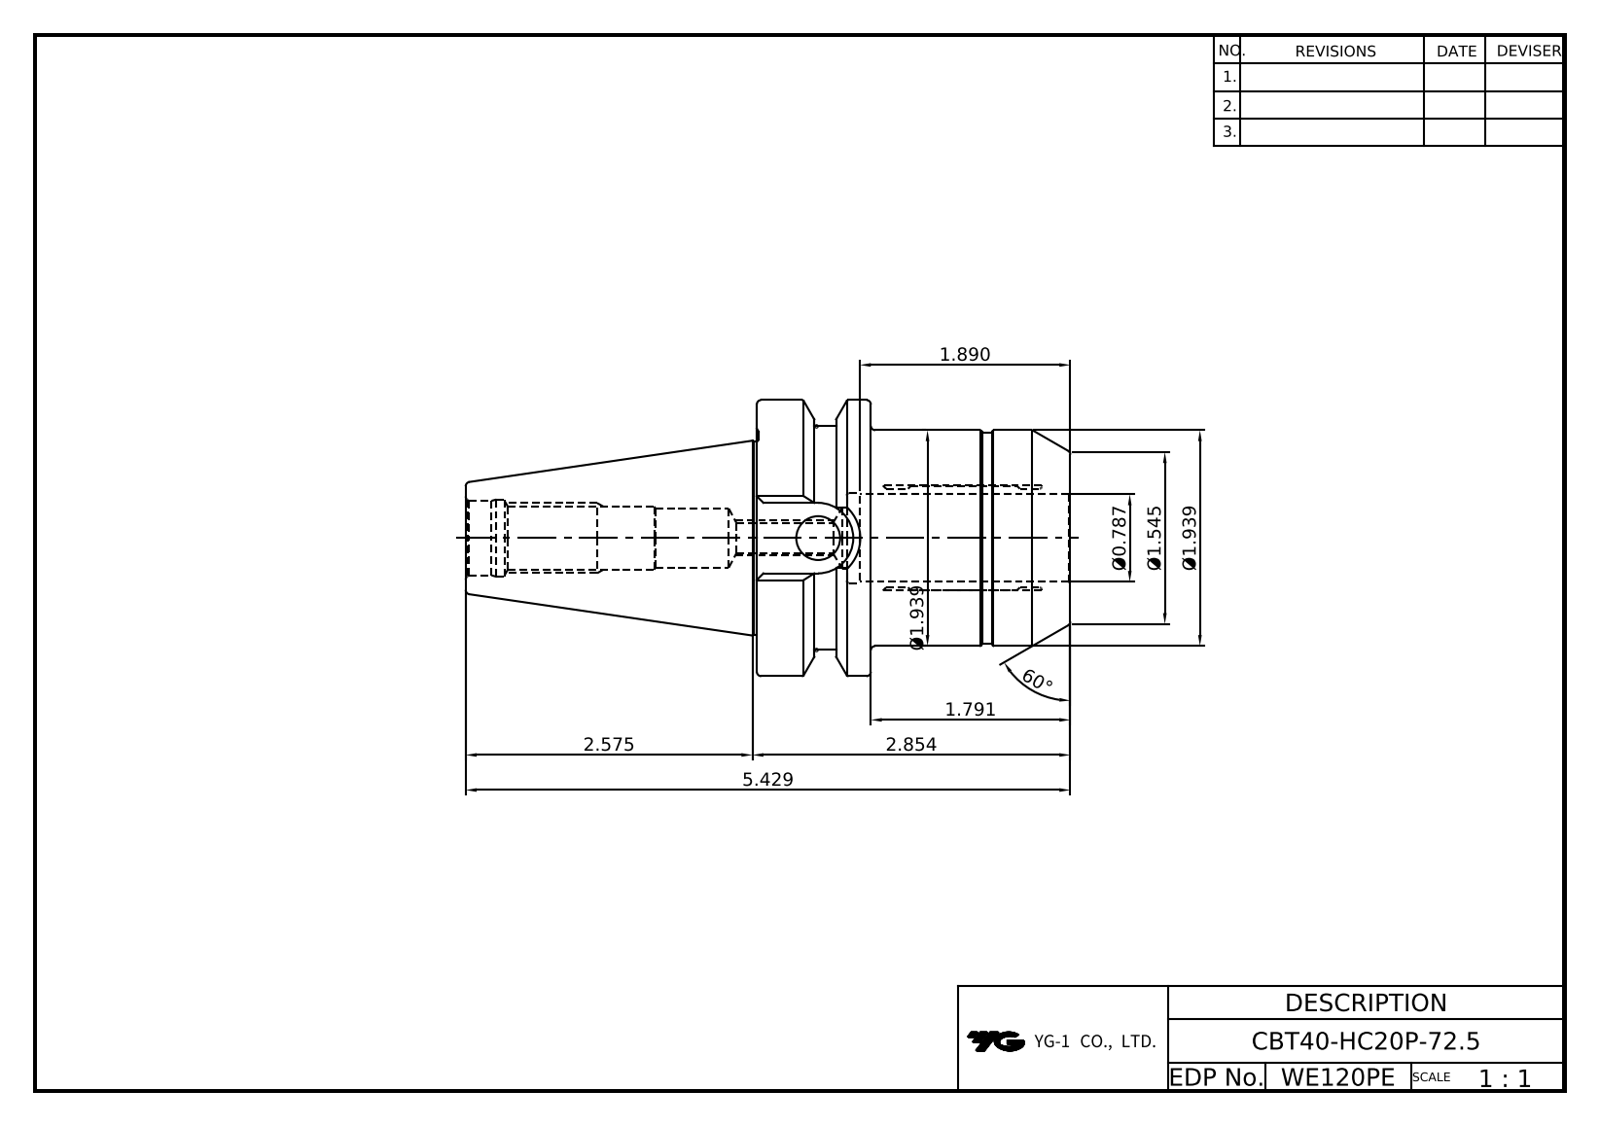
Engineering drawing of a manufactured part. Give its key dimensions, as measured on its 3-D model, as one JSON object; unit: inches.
{"part_name": "LO-CBT40-HC20P-72.5", "step_written_by": "Autodesk Inventor 2020 (AUTOMOTIVE_DESIGN)", "units": "inches", "bodies": {"solids": 1, "faces": 74, "planar": 24, "cylindrical": 19, "other": 31}, "overall_size": [5.429, 2.48, 2.48], "volume_in3": 11.66, "surface_area_in2": 49.04, "round_holes": [[0.272, 1], [0.531, 1], [0.545, 1], [0.551, 1], [0.669, 1], [0.693, 1], [0.787, 1], [0.807, 1]], "round_bosses_or_shafts": [[2.48, 1], [2.008, 1], [1.939, 1], [1.9, 1], [1.732, 1]], "partial_cylinders_radius": [[0.317, 1]], "face_to_face_distances": [1.791, 1.024, 2.815, 1.78, 0.713, 0.311, 2.102, 0.516, 0.197, 0.508]}
